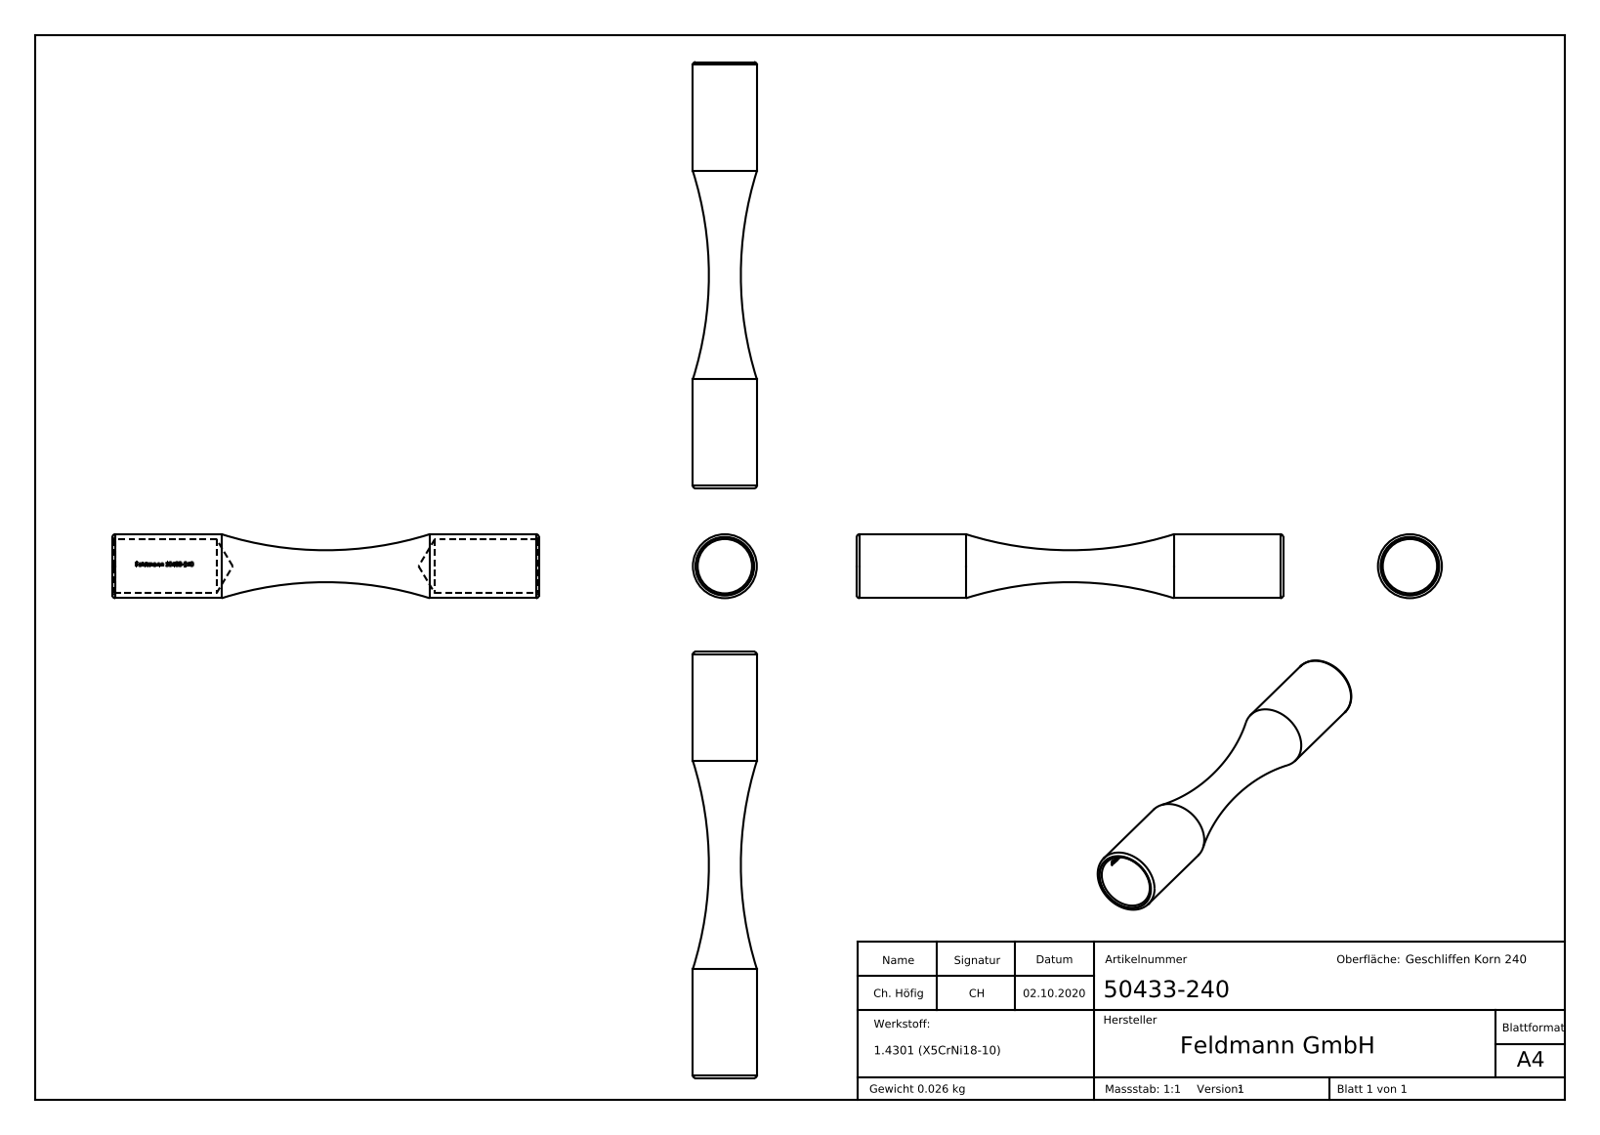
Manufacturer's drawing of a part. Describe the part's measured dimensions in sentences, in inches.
The part is named "50433-240". Its 3-D file was written by "SolidWorks 2018 (CONFIG_CONTROL_DESIGN)". It is 1 solid with 274 faces: 104 planar, 46 cylindrical and 124 other. Overall it measures 3.15 by 0.472 by 0.472 inches. Its volume is 0.203 cubic inches and its surface area 6.237 square inches. Round holes: 1 of diameter 0.402. Round bosses or shafts: 1 of diameter 0.472. Partial cylindrical surfaces (rounded edges, fillets, slot ends): 1 of radius 0.205. The main face-to-face distances are 3.15, 0.07, 0.021, 0.048, 0.03, 0.111, 0.345, 0.235, 0.039, 0.017.
